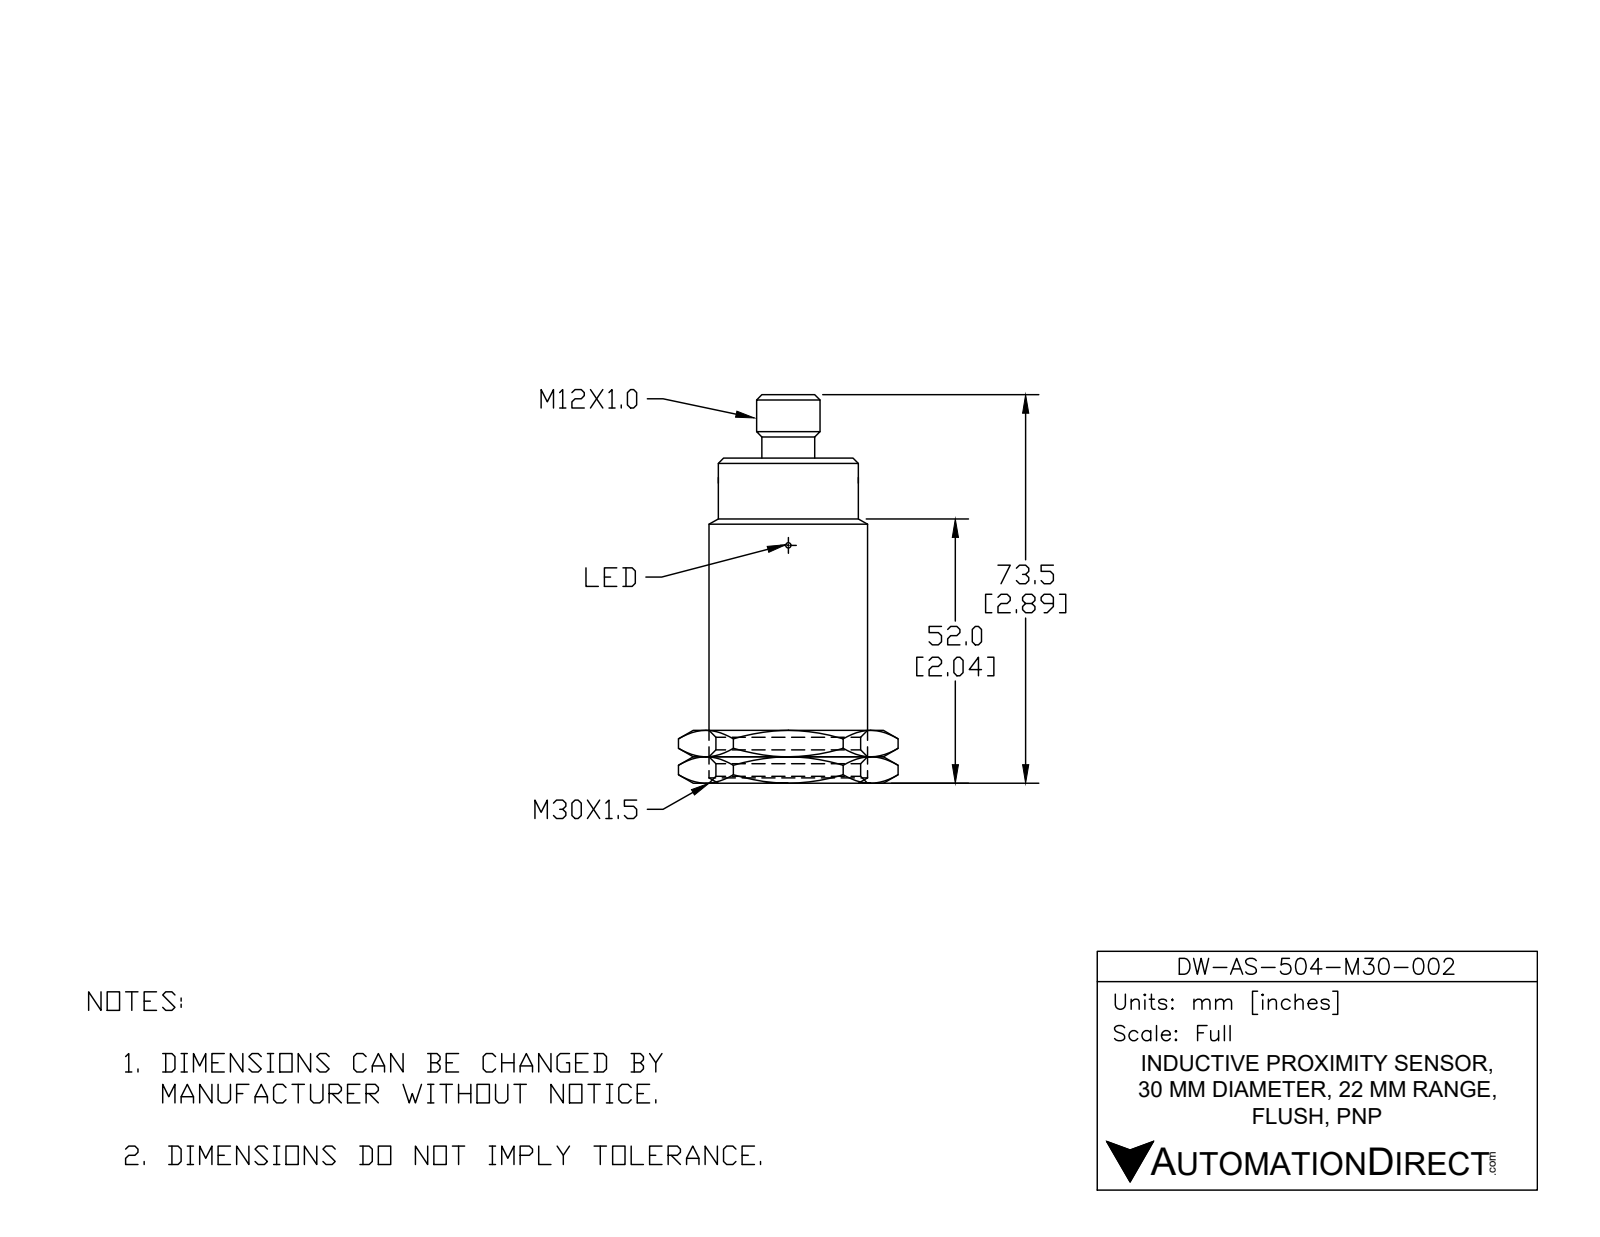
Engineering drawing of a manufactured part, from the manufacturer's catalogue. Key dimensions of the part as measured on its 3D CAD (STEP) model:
Part name (STEP PRODUCT): DW-AS-514-M30-002
STEP written by: SolidWorks 2017 (AUTOMOTIVE_DESIGN)
Units: inches
Bodies: 1 solid, 38 faces (8 planar, 20 cylindrical, 10 other)
Overall size (bounding box): 2.895 × 1.181 × 1.181
Volume: 2.6 in³ · Surface area: 12.11 in²
Round holes (diameter × count): ⌀0.118 ×2, ⌀0.335 ×1
Round bosses / shafts (diameter × count): ⌀0.039 ×4, ⌀1.181 ×1, ⌀1.083 ×1, ⌀0.472 ×1, ⌀0.415 ×1
Partial cylindrical surfaces — rounded edges, fillets, slot ends (radius × count): R0.022 ×2, R0.193 ×1
Main face-to-face distances: 2.38, 2.552, 0.172, 2.05, 0.33, 0.502, 2.895, 0.845, 0.515, 0.343
